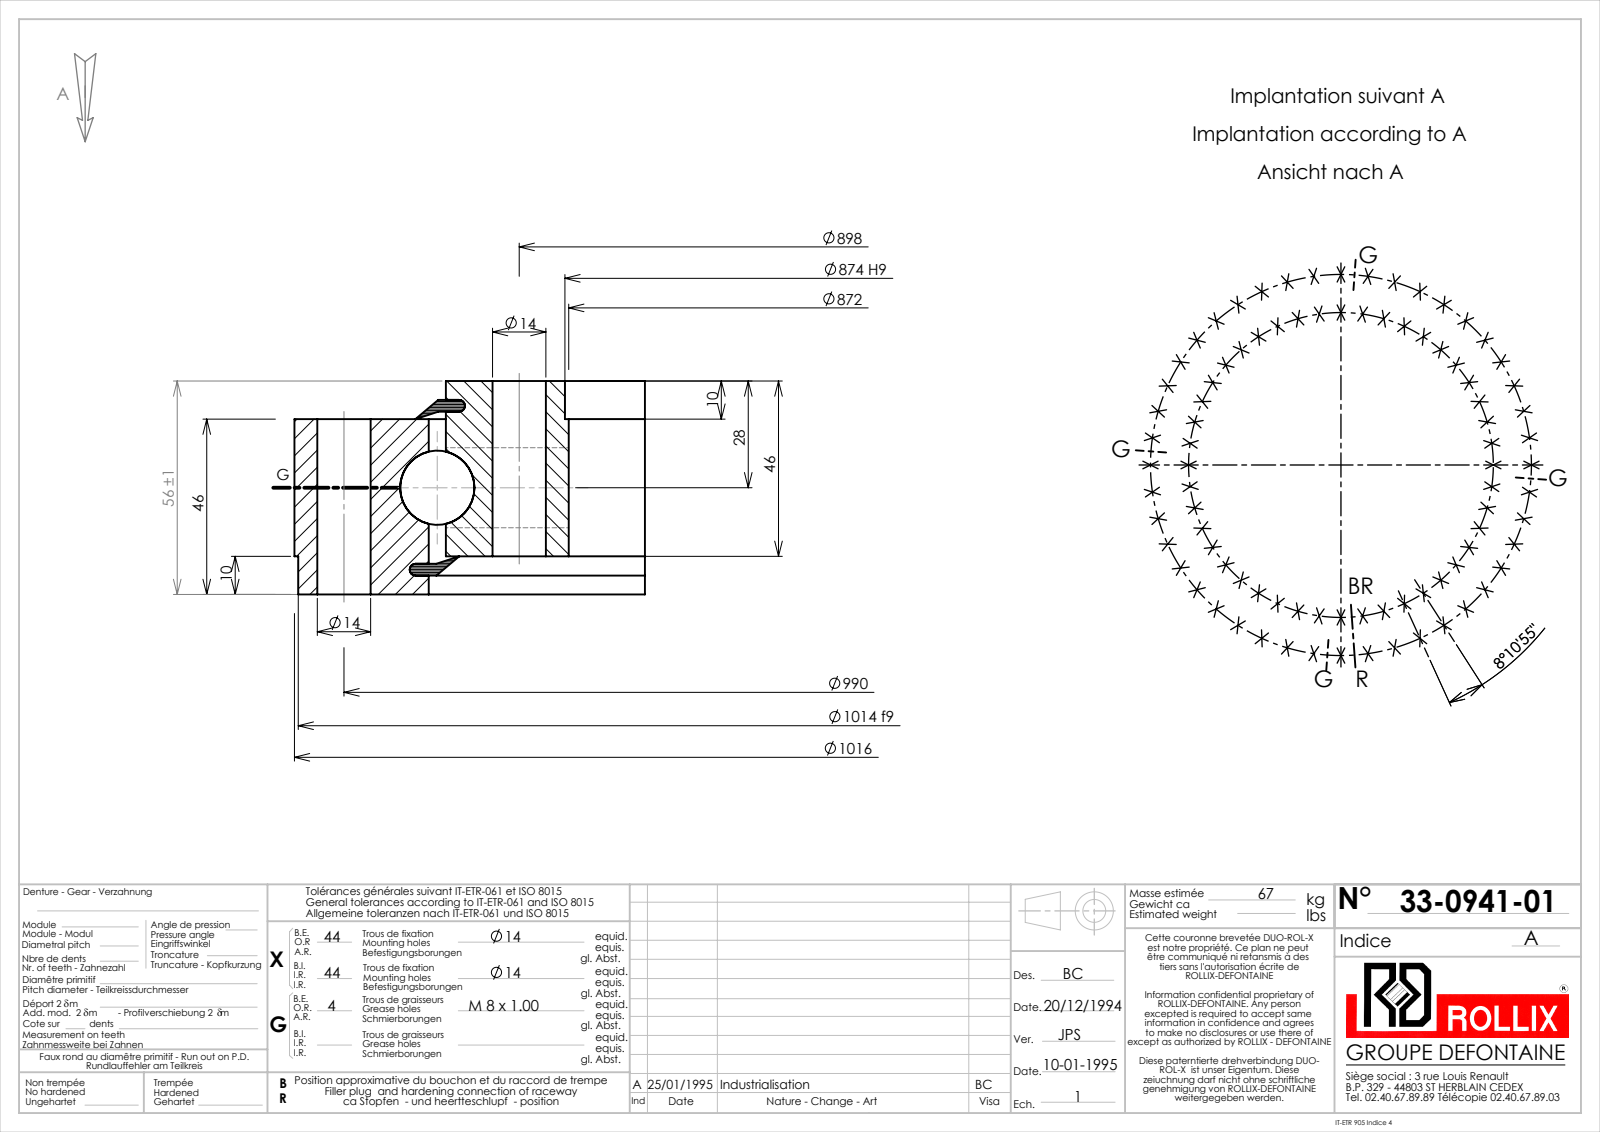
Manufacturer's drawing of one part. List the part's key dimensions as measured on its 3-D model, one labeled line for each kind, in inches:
Part name (STEP PRODUCT): 33-0941-01
STEP written by: SolidWorks 2016 (CONFIG_CONTROL_DESIGN)
Units: inches
Bodies: 9 solids, 334 faces (54 planar, 212 cylindrical, 68 other)
Overall size (bounding box): 40.668 × 40.668 × 2.205
Volume: 487.9 in³ · Surface area: 2 127 in²
Round holes (diameter × count): ⌀0.551 ×88, ⌀0.276 ×4, ⌀34.331 ×1, ⌀34.409 ×1, ⌀37.224 ×1
Round bosses / shafts (diameter × count): ⌀0.315 ×4, ⌀40 ×1, ⌀39.921 ×1, ⌀36.87 ×1
Main face-to-face distances: 1.811, 0.394, 1.417, 2.205, 0.317, 1.888, 0.077, 1.494, 0.195, 2.01
Hole centre spacings: 2.522, 5.031, 21.187, 14.687, 7.515, 26.719, 12.355, 9.96
